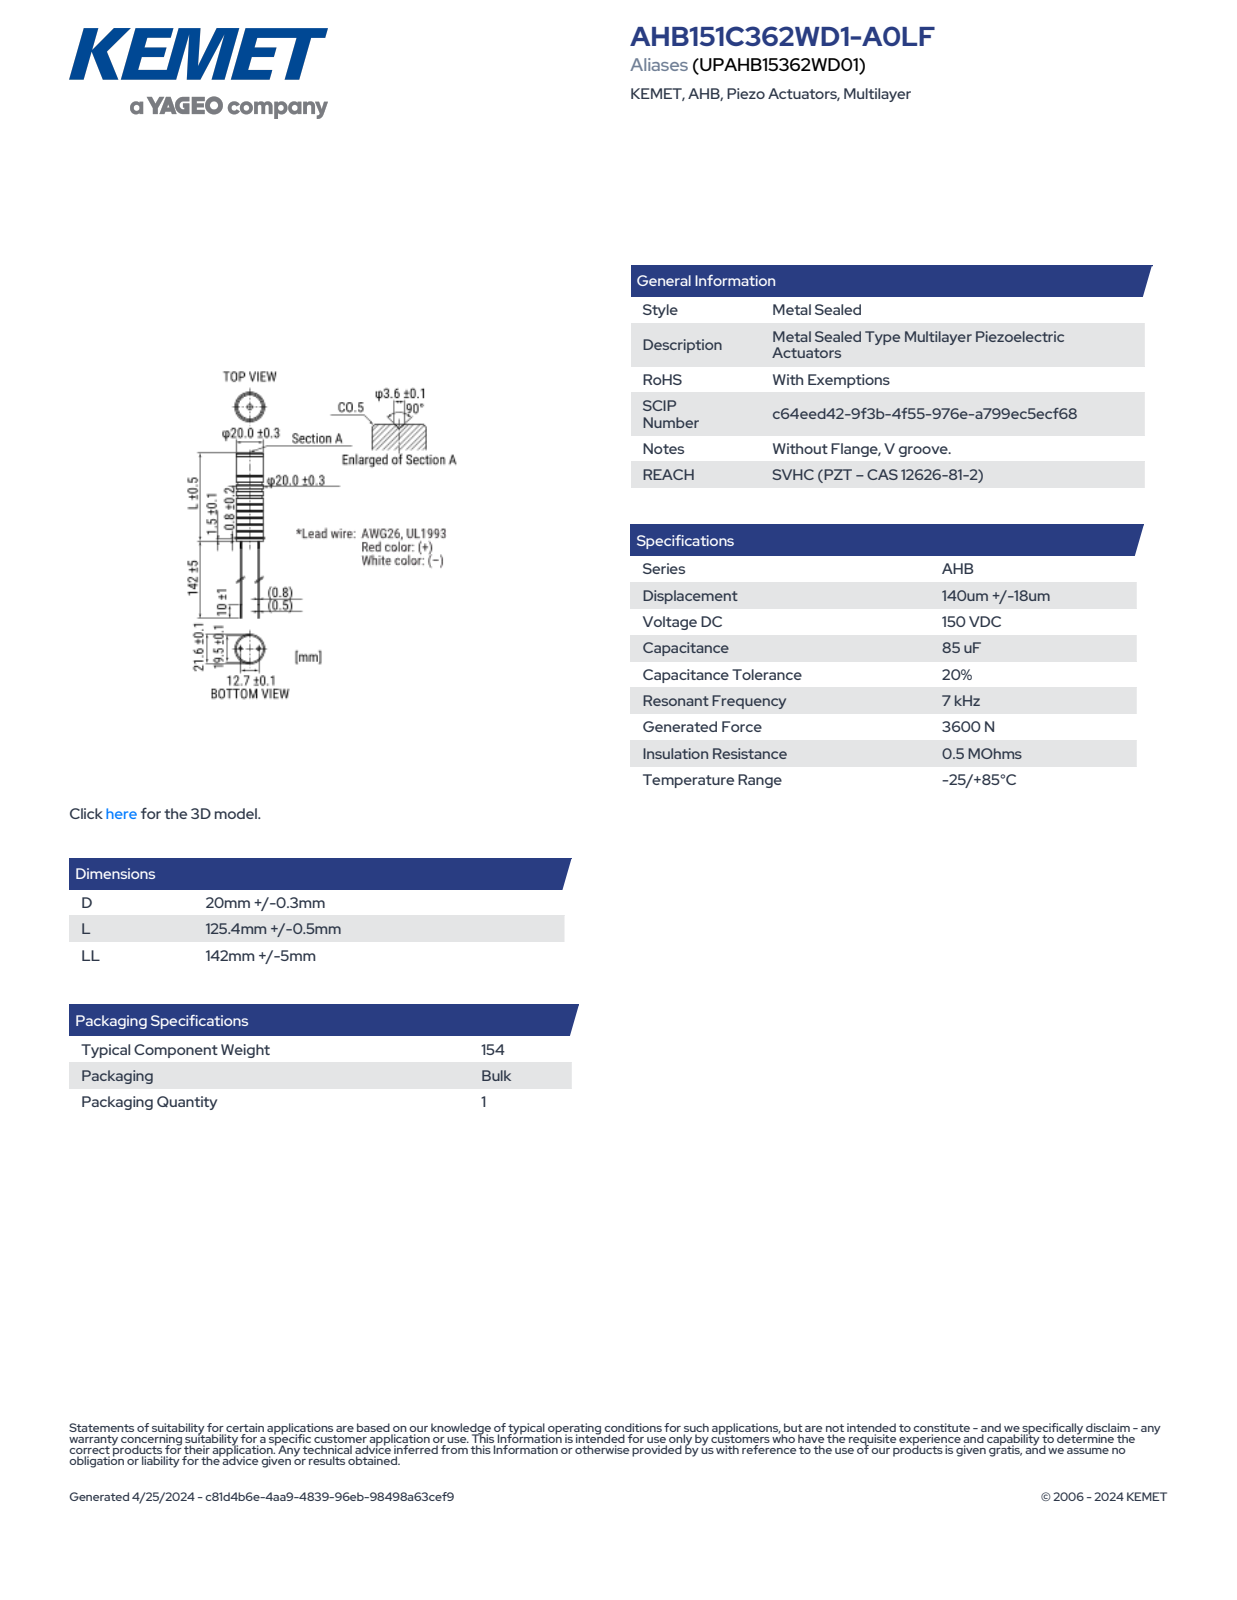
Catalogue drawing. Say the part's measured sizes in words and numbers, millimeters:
The part is named "AL_KAHBASB_D20.3L125.9". Its 3-D file was written by "SolidWorks 2014 (AUTOMOTIVE_DESIGN)". It is 2 solids with 131 faces: 65 planar, 34 cylindrical and 32 other. Overall it measures 272.9 by 21.7 by 21.7 millimeters. Its volume is 40 139 cubic millimeters and its surface area 10 634 square millimeters. Round bosses or shafts: 2 of diameter 1, 2 of diameter 0.8, 1 of diameter 21.7, 1 of diameter 20.3, 1 of diameter 19.6, 1 of diameter 0.6, 1 of diameter 0.5. The main face-to-face distances are 123.3, 2.6, 125.9, 1.6, 1, 124.3, 125.91, 124.31, 123.31, 10.
